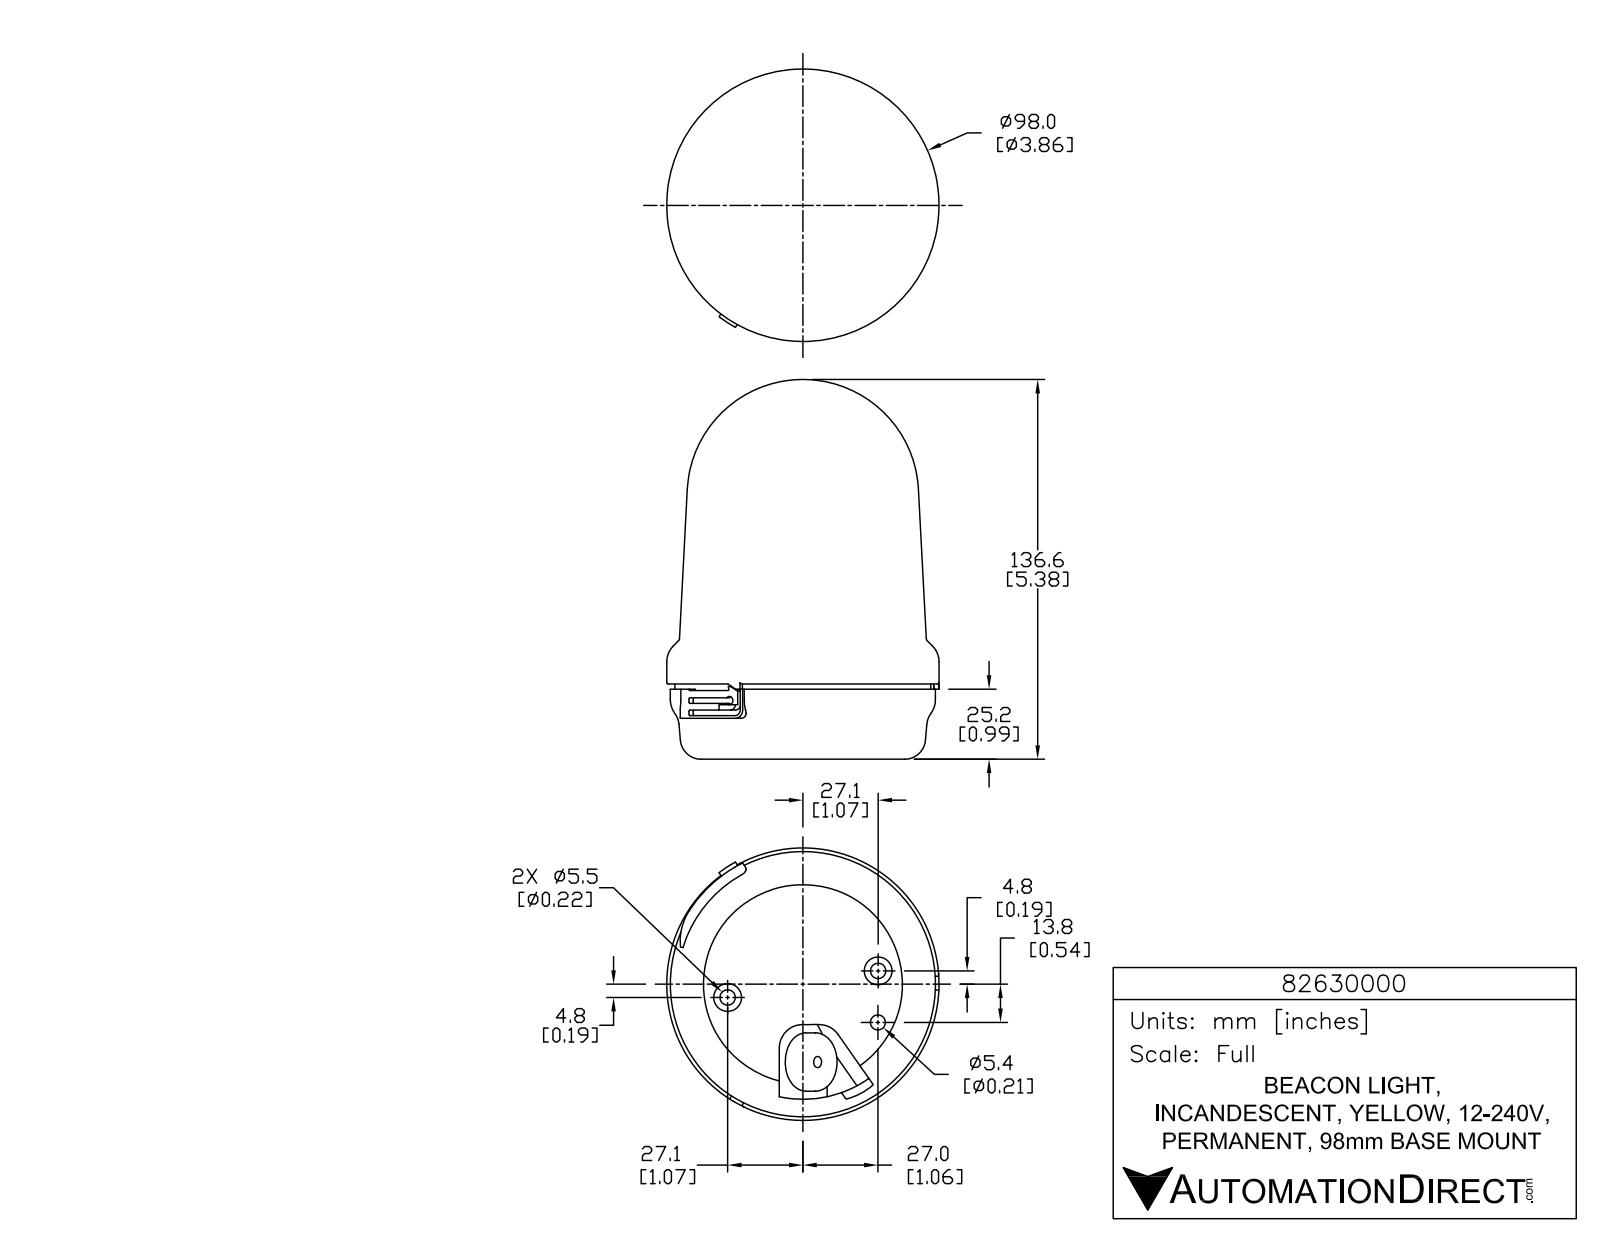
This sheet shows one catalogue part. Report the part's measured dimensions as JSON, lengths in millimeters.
{"part_name": "82630000", "step_written_by": "SolidWorks 2015 (AUTOMOTIVE_DESIGN)", "units": "millimeters", "bodies": {"solids": 1, "faces": 872, "planar": 566, "cylindrical": 204, "other": 102}, "overall_size": [136.6, 98, 98], "volume_mm3": 732300, "surface_area_mm2": 47520, "round_holes": [[1.5, 3], [5.5, 2], [4, 1], [5.4, 1], [71.6, 1]], "round_bosses_or_shafts": [[8.6, 3], [2.1, 3], [10, 2], [98, 1], [95.4, 1], [92.1, 1], [21, 1]], "partial_cylinders_radius": [[0.1, 9], [0.1, 6], [0.3, 6], [0.3, 6], [0.3, 6], [5, 6], [0.5, 5], [1, 4]], "face_to_face_distances": [26.5, 24.7, 1.9, 0.5, 25.2, 27.1, 6, 14.7, 14.2, 10.5], "hole_center_spacings": [27.5, 18.5, 30.3, 54.8, 55]}
